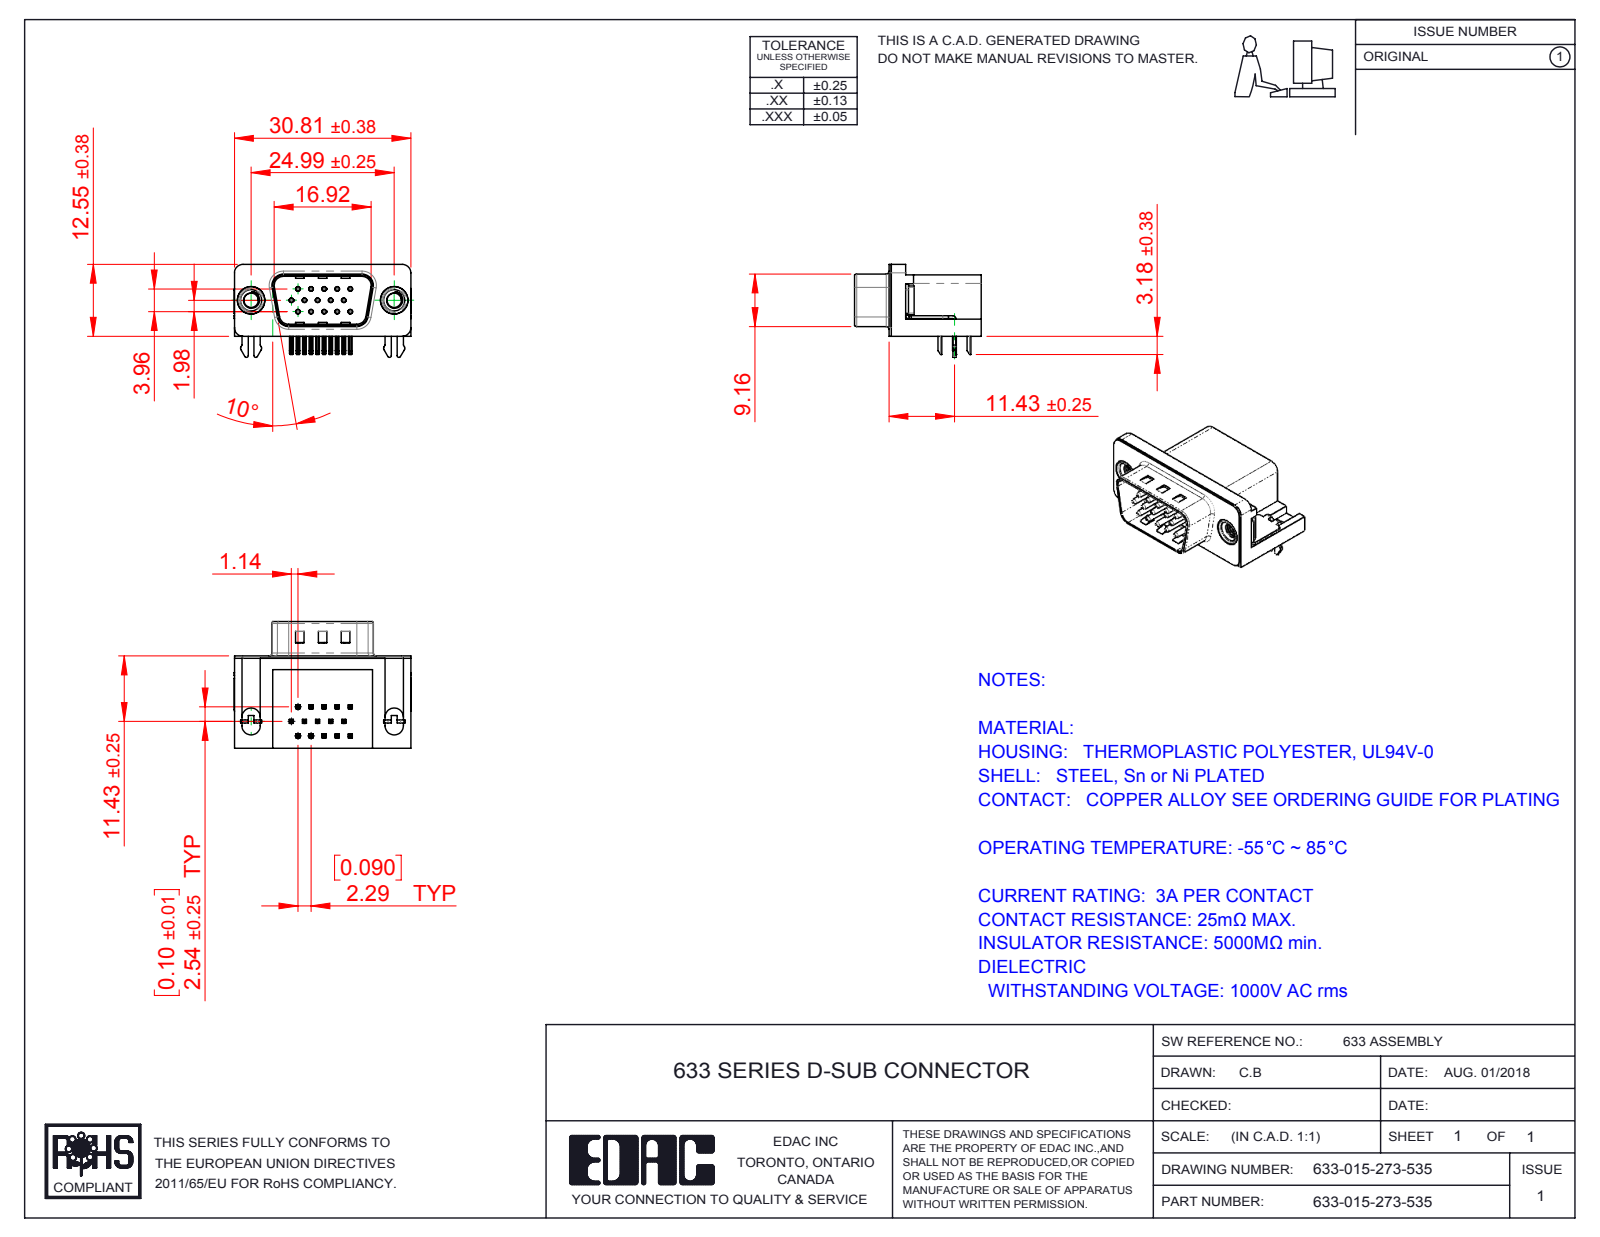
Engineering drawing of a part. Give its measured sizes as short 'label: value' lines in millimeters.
name: 633 Contact Top; 633 Contact Bottom; 633 Shell_15 Contact; 633 M3 Threaded Rivet (+5 more)
written by: SolidWorks 2016 (CONFIG_CONTROL_DESIGN)
unit: mm
bodies: 21 solids, 1483 faces (893 planar, 455 cylindrical, 135 other)
size: 30.89 × 22.1 × 16.25
volume: 4 067 mm³; area: 5 429 mm²
holes: 15× ⌀0.35, 15× ⌀0.8, 2× ⌀2.5, 2× ⌀4, 2× ⌀4.8, 2× ⌀5
bosses: 15× ⌀0.75, 2× ⌀4.9, 2× ⌀4.75, 2× ⌀3.9
rounds: 68× R0.25, 30× R0.12, 16× R1, 14× R0.5, 8× R1.6, 7× R1.5, 4× R0.32, 4× R0.9
face distances: 0.4, 10.35, 15.7, 2.9, 0.5, 6.7, 16.1, 2.5, 0.35, 10.7
hole spacings: 3.96, 2.28, 4.57, 2.29, 6.05, 6.86, 7.92, 6.04
